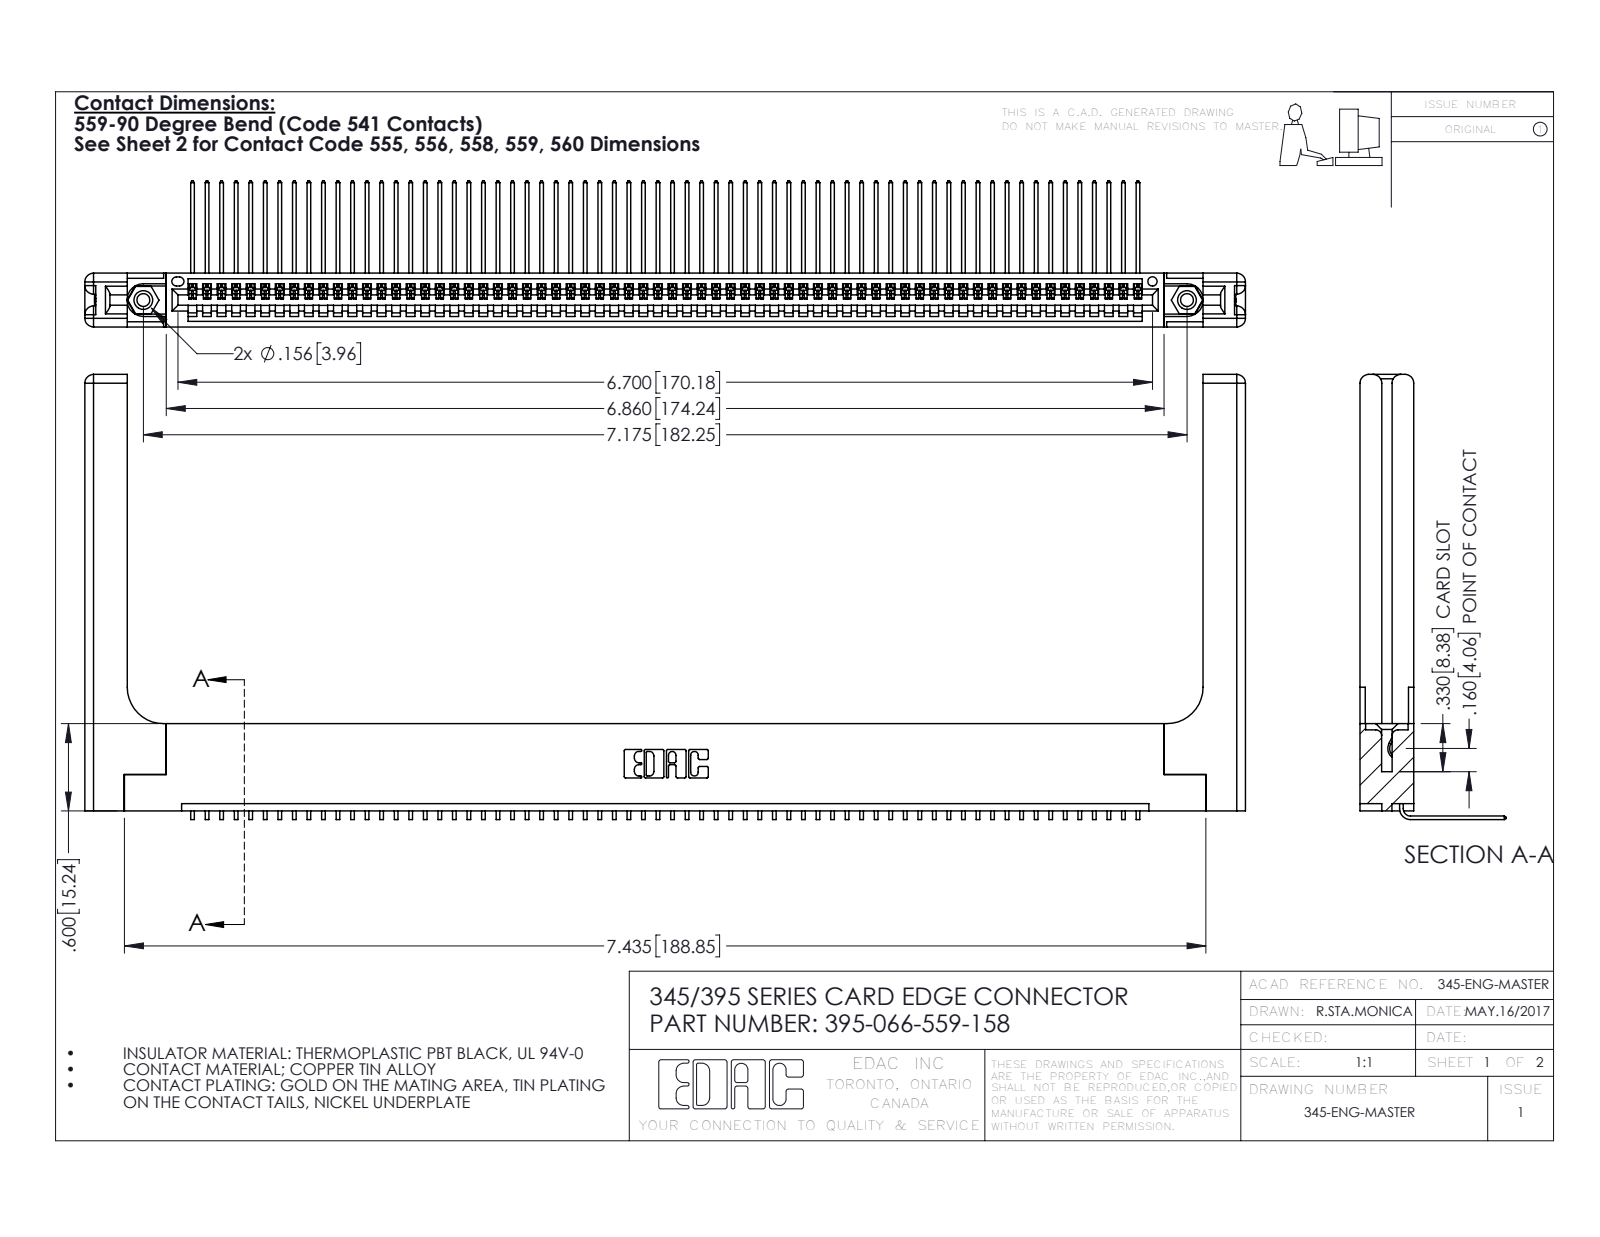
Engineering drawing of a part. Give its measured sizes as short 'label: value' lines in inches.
name: 345-250-001_345-250-001-102; 345 Part_Flush Mounting Lugs - 0.156 Dia-TH; 395-066-559-158; 345-292-001_558 559 Tail - 1 (+1 more)
written by: SolidWorks 2016 (CONFIG_CONTROL_DESIGN)
unit: in
bodies: 71 solids, 4342 faces (3000 planar, 1282 cylindrical, 60 other)
size: 7.979 × 3.059 × 1.005
volume: 1.719 in³; area: 51.24 in²
holes: 2× ⌀0.089, 2× ⌀0.125, 2× ⌀0.156, 1× ⌀0.064
bosses: 2× ⌀0.155
rounds: 132× R0.006, 22× R0.01, 16× R0.06, 6× R0.007, 6× R0.031, 3× R0.026, 2× R0.03, 2× R0.031
face distances: 0.072, 0.37, 0.298, 0.2, 0.098, 0.272, 0.025, 0.225, 0.148, 0.15
hole spacings: 0.27, 6.939, 7.175
